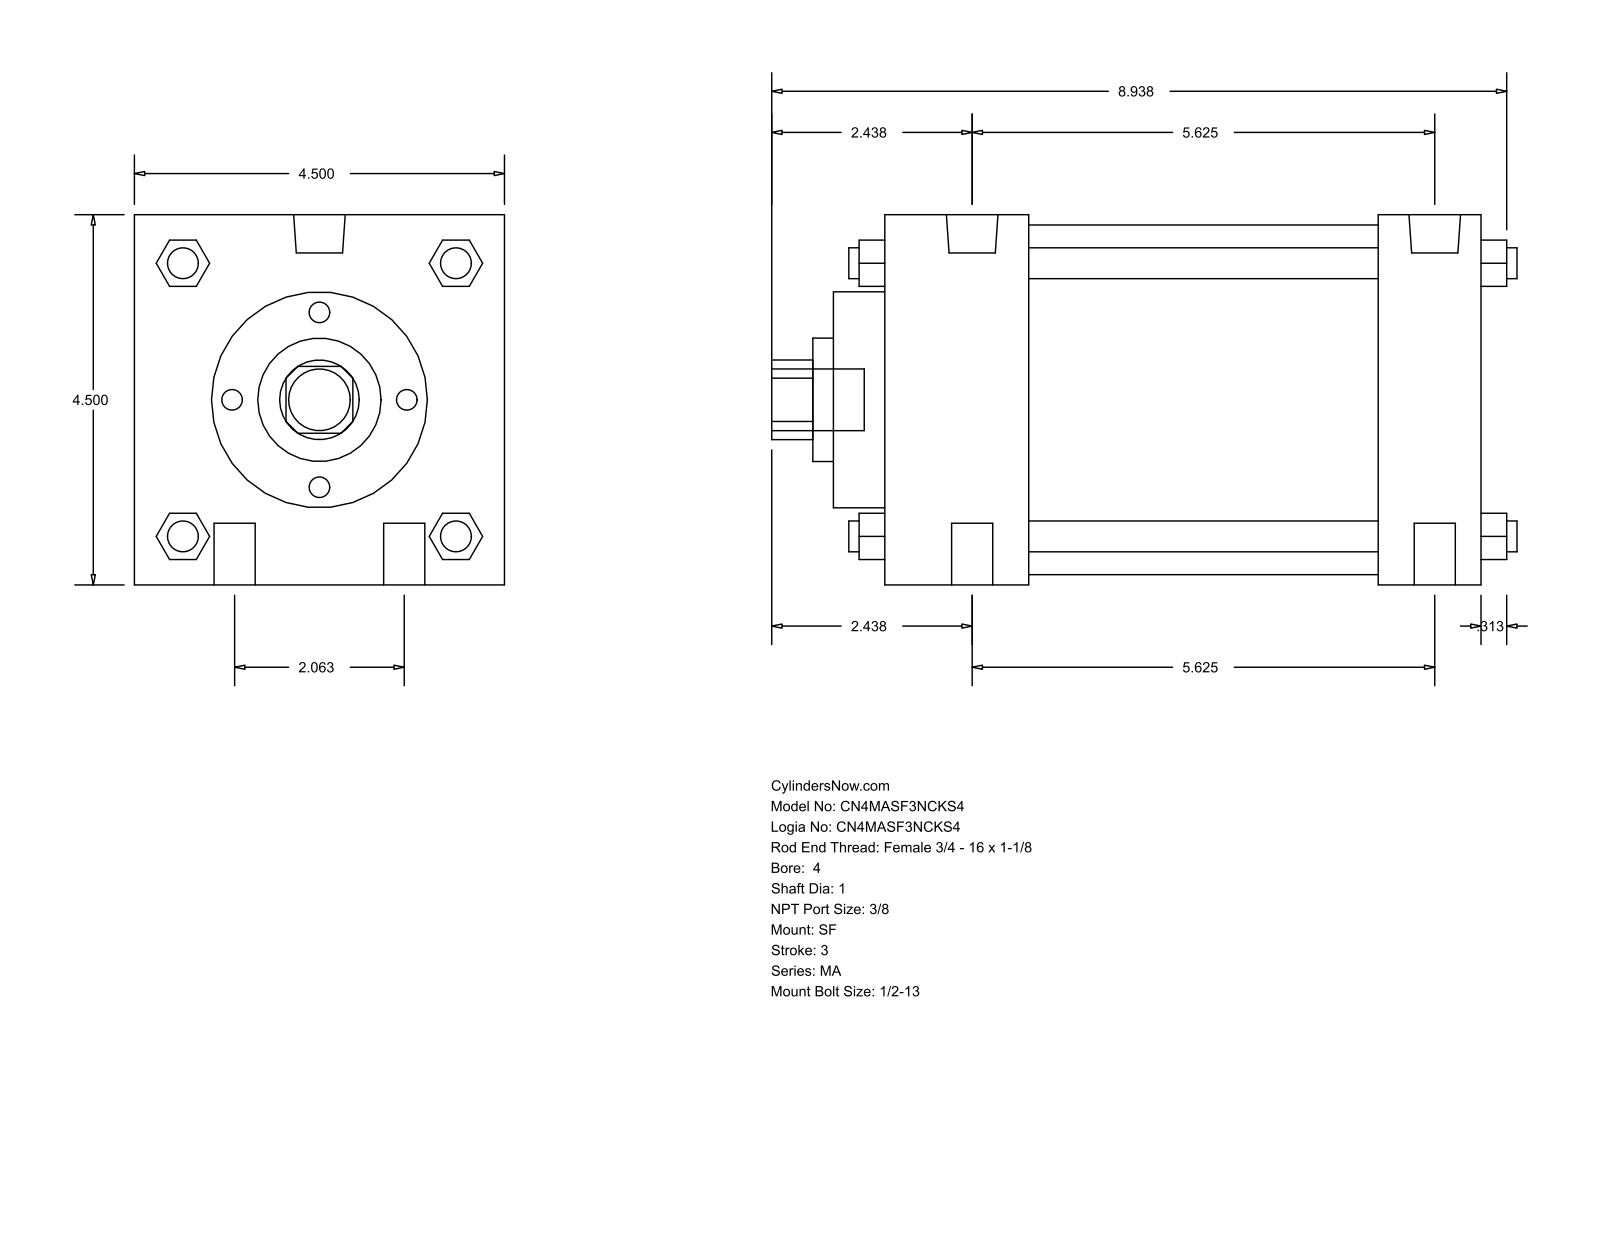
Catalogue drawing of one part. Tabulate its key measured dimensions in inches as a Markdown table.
| quantity | value |
| --- | --- |
| part name | MA_SF__0400_1 |
| STEP written by | GSSL Pune (CONFIG_CONTROL_DESIGN) |
| units | inches |
| bodies | 0 solids, 126 faces (95 planar, 31 cylindrical, 0 other) |
| overall size | 9.063 × 4.5 × 4.5 |
| round holes (diameter × count) | 1 × 1, 1.5 × 1, 2.625 × 1, 4.25 × 1 |
| round bosses / shafts (diameter × count) | 0.5 × 4, 0.375 × 4, 0.627 × 2, 0.437 × 2, 0.75 × 1 |
| partial cylindrical surfaces (radius × count) | 0.484 × 1 |
| main face-to-face distances | 4.5, 7.25, 6, 1.25, 1.75, 4.25, 5.5, 7.875, 0.625, 2.375 |
